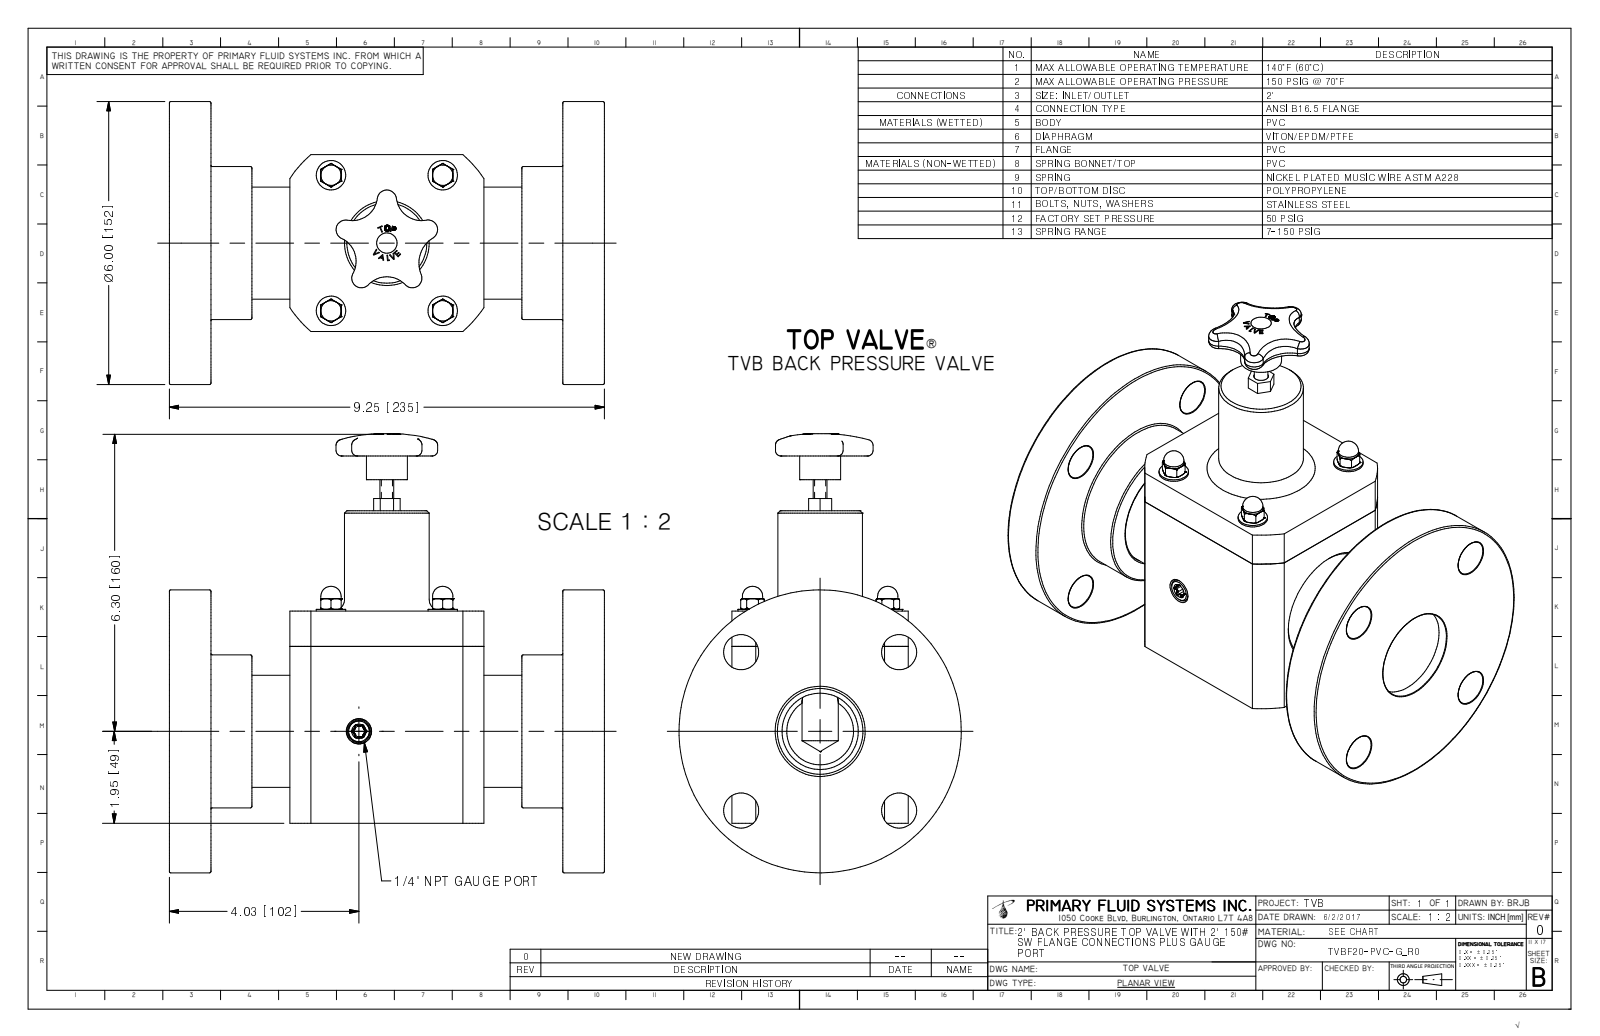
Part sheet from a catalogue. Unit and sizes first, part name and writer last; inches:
Units: inches
Overall size (bounding box): 9.312 × 9.25 × 6
Round holes (diameter × count): ⌀0.175 ×4, ⌀0.745 ×4, ⌀0.188 ×1, ⌀0.437 ×1, ⌀1.913 ×1, ⌀1.939 ×1
Round bosses / shafts (diameter × count): ⌀0.625 ×4, ⌀0.433 ×4, ⌀0.375 ×4, ⌀6 ×1, ⌀3.244 ×1, ⌀2.375 ×1, ⌀1.8 ×1, ⌀0.87 ×1
Partial cylindrical surfaces — rounded edges, fillets, slot ends (radius × count): R0.027 ×6, R0.085 ×5, R0.205 ×5, R0.536 ×4, R0.656 ×4, R0.625 ×1, R0.745 ×1, R2.475 ×1
Main face-to-face distances: 0.885, 8.365, 9.25, 7.48, 2.563, 6.688, 1.678, 5.803, 3.75, 4.5
Hole centre spacings: 2.375, 3.359, 2.375, 2.875, 3.729, 4.75
Volume: 122 in³ · Surface area: 384.1 in²
Bodies: 1 solid, 421 faces (161 planar, 70 cylindrical, 190 other)
Part name (STEP PRODUCT): TVBF20-PVC-G_R0
STEP written by: Autodesk Inventor 2009 (AUTOMOTIVE_DESIGN)
